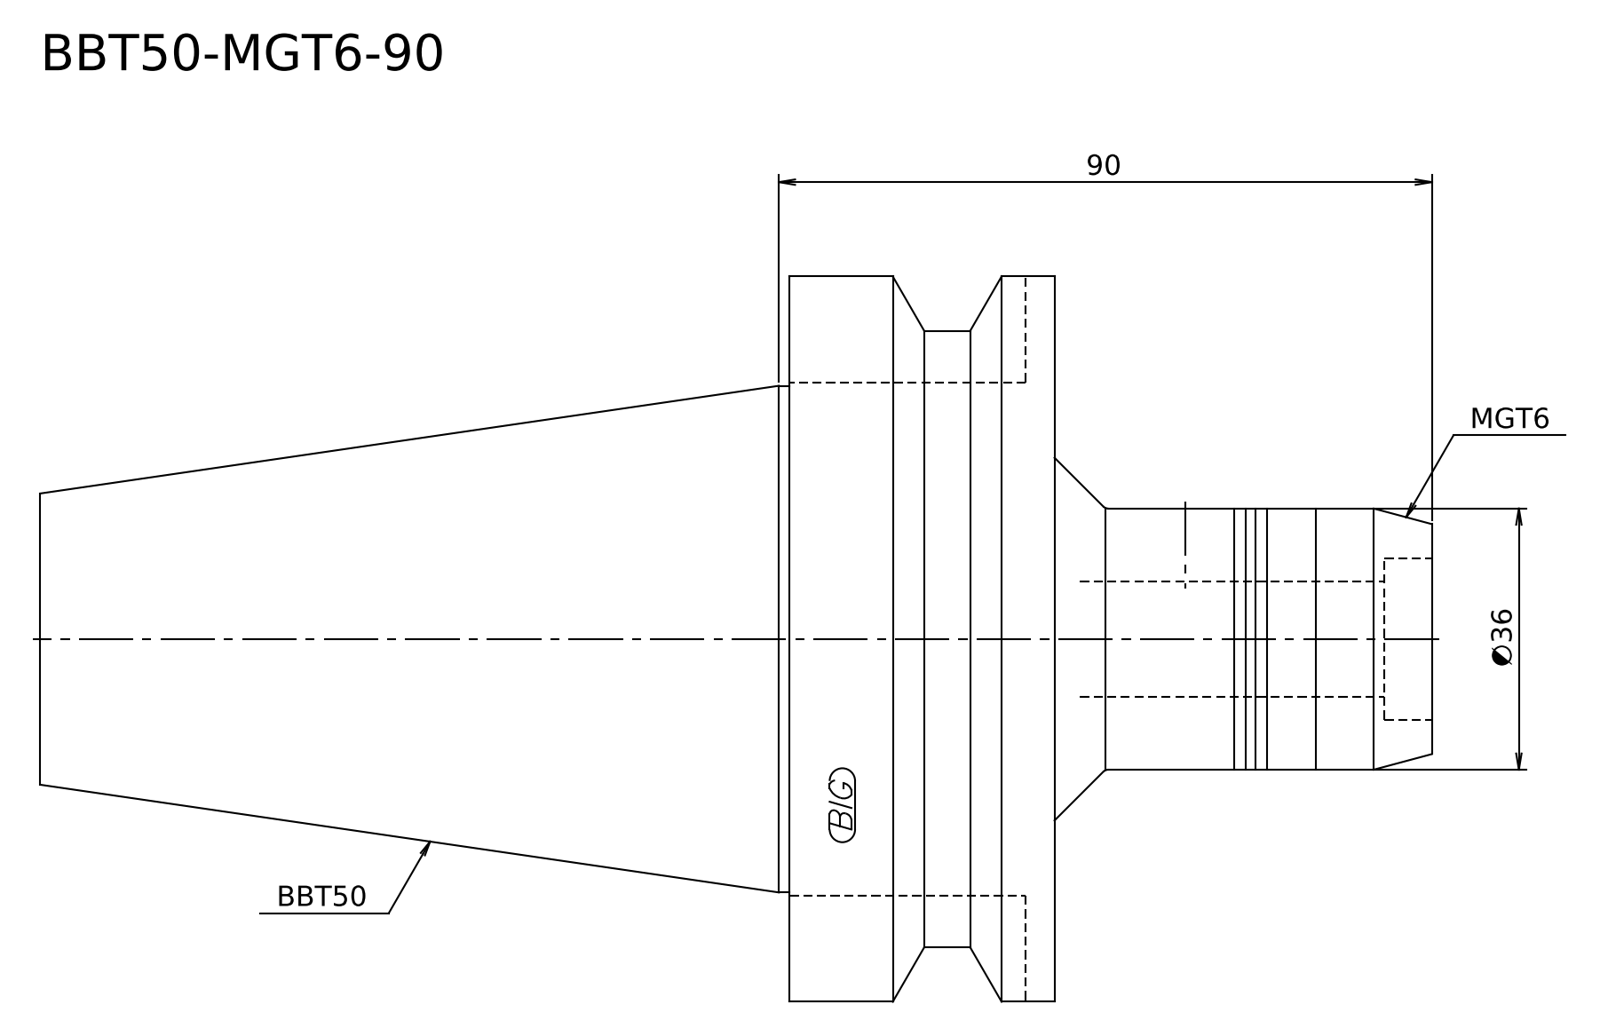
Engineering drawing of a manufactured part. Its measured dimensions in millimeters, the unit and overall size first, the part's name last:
Units: millimetres
Overall size (bounding box): 191.8 × 100 × 100
Round bosses / shafts (diameter × count): ⌀100 ×1, ⌀85 ×1, ⌀69.85 ×1, ⌀36 ×1
Main face-to-face distances: 36.5, 139.8, 103.3, 52, 88.5, 191.8
Volume: 571 807 mm³ · Surface area: 49 959 mm²
Bodies: 1 solid, 14 faces (4 planar, 5 cylindrical, 5 other)
STEP written by: Kubotek KeyCreator V8.5.1 (14335) (CONFIG_CONTROL_DESIGN)
